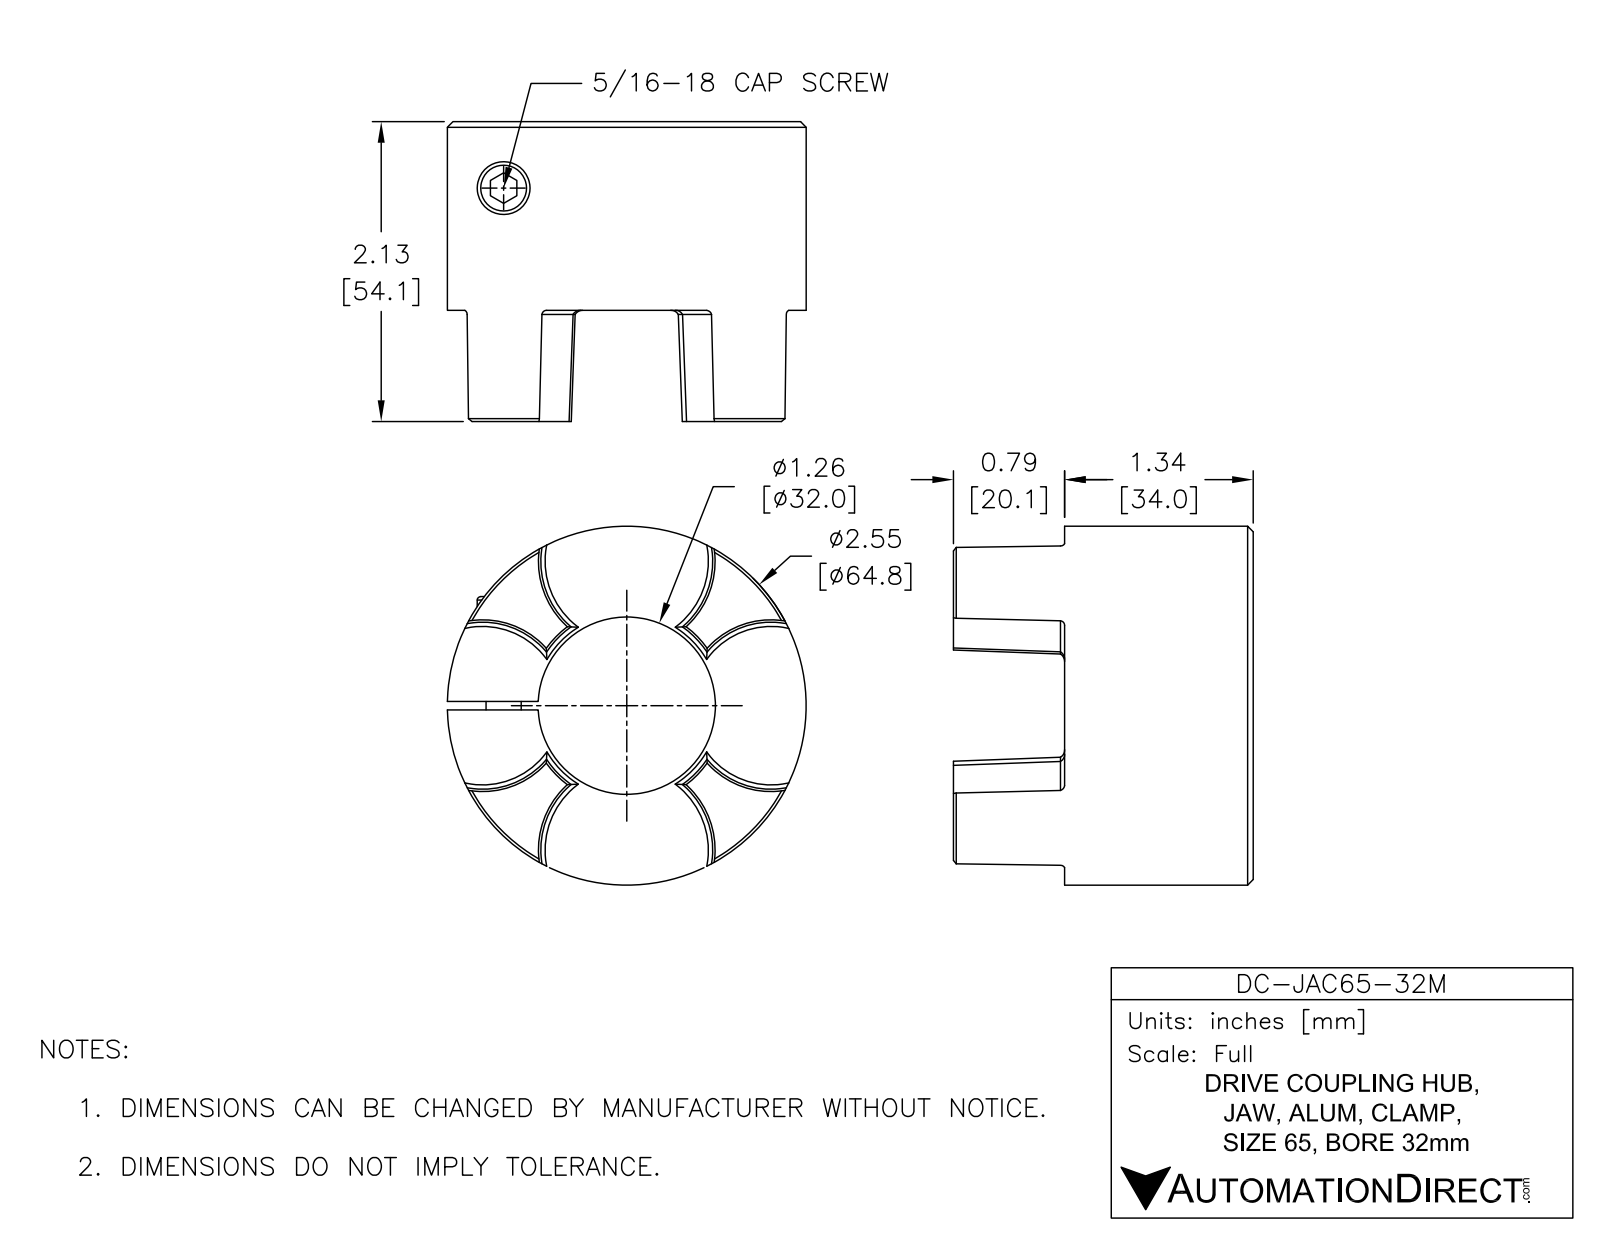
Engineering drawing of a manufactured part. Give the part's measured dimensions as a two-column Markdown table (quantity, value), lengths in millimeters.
| quantity | value |
| --- | --- |
| part name | DC-JAC65-32M |
| STEP written by | SolidWorks 2015 (AUTOMOTIVE_DESIGN) |
| units | millimeters |
| bodies | 1 solid, 55 faces (9 planar, 9 cylindrical, 37 other) |
| overall size | 64.77 × 64.76 × 54.1 |
| volume | 94 604 mm³ |
| surface area | 21 134 mm² |
| round holes (diameter × count) | 6.76 × 1, 10.31 × 1, 32 × 1 |
| round bosses / shafts (diameter × count) | 64.77 × 1 |
| main face-to-face distances | 34.04, 54.1, 20.06, 1.52, 14.09, 12.57 |
